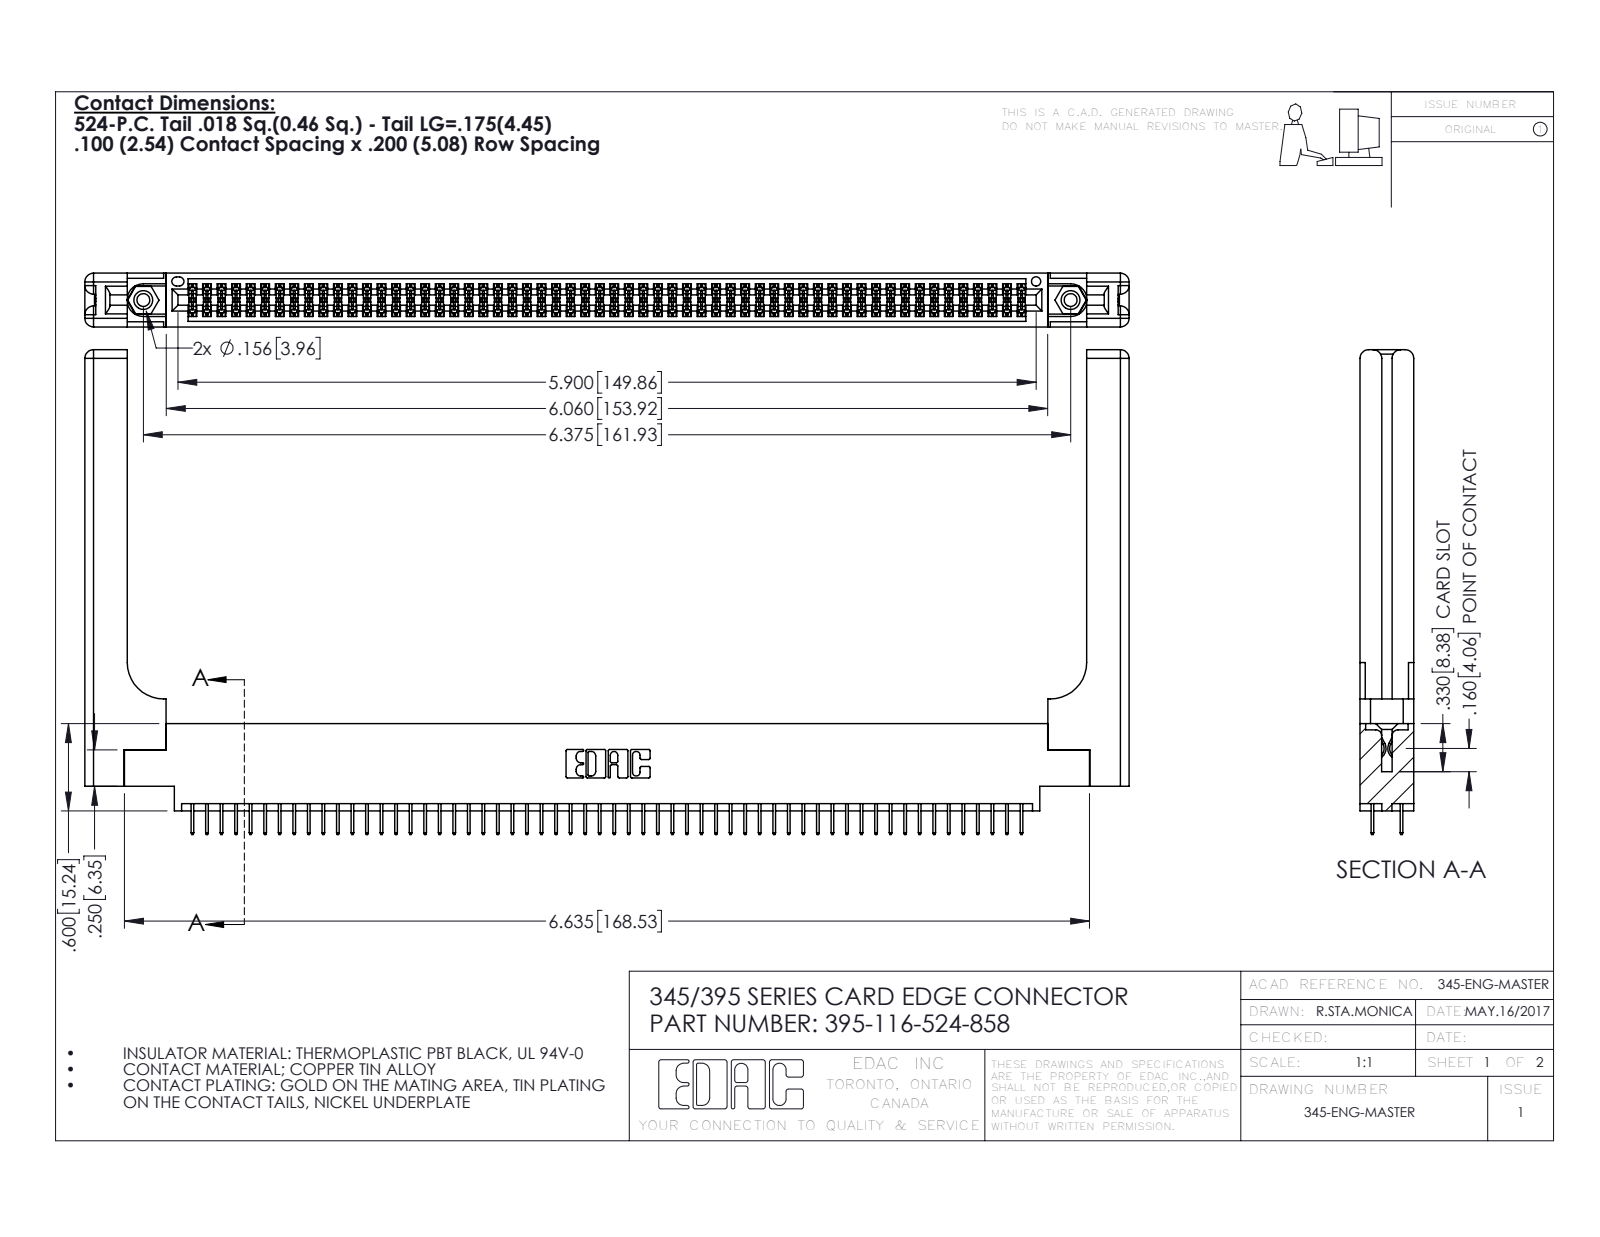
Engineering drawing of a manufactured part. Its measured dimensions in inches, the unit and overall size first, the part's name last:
Units: inches
Overall size (bounding box): 7.179 × 3.332 × 0.37
Round holes (diameter × count): ⌀0.089 ×2, ⌀0.125 ×2, ⌀0.156 ×2, ⌀0.064 ×1
Round bosses / shafts (diameter × count): ⌀0.155 ×2
Partial cylindrical surfaces — rounded edges, fillets, slot ends (radius × count): R0.006 ×174, R0.01 ×22, R0.06 ×16, R0.007 ×6, R0.031 ×6, R0.026 ×3, R0.014 ×2, R0.019 ×2
Main face-to-face distances: 0.072, 0.37, 0.298, 0.2, 0.098, 0.272, 0.025, 0.225, 0.175, 0.148
Hole centre spacings: 0.27, 6.139, 6.375
Volume: 1.59 in³ · Surface area: 48.09 in²
Bodies: 121 solids, 6650 faces (4756 planar, 1834 cylindrical, 60 other)
Part name (STEP PRODUCT): 345 Part_0.170 Offset - 0.156 Dia-TH; 345-292-001_345-293-124; 395-116-524-858; 345-220-058_345-220-058 (+1 more)
STEP written by: SolidWorks 2016 (CONFIG_CONTROL_DESIGN)
